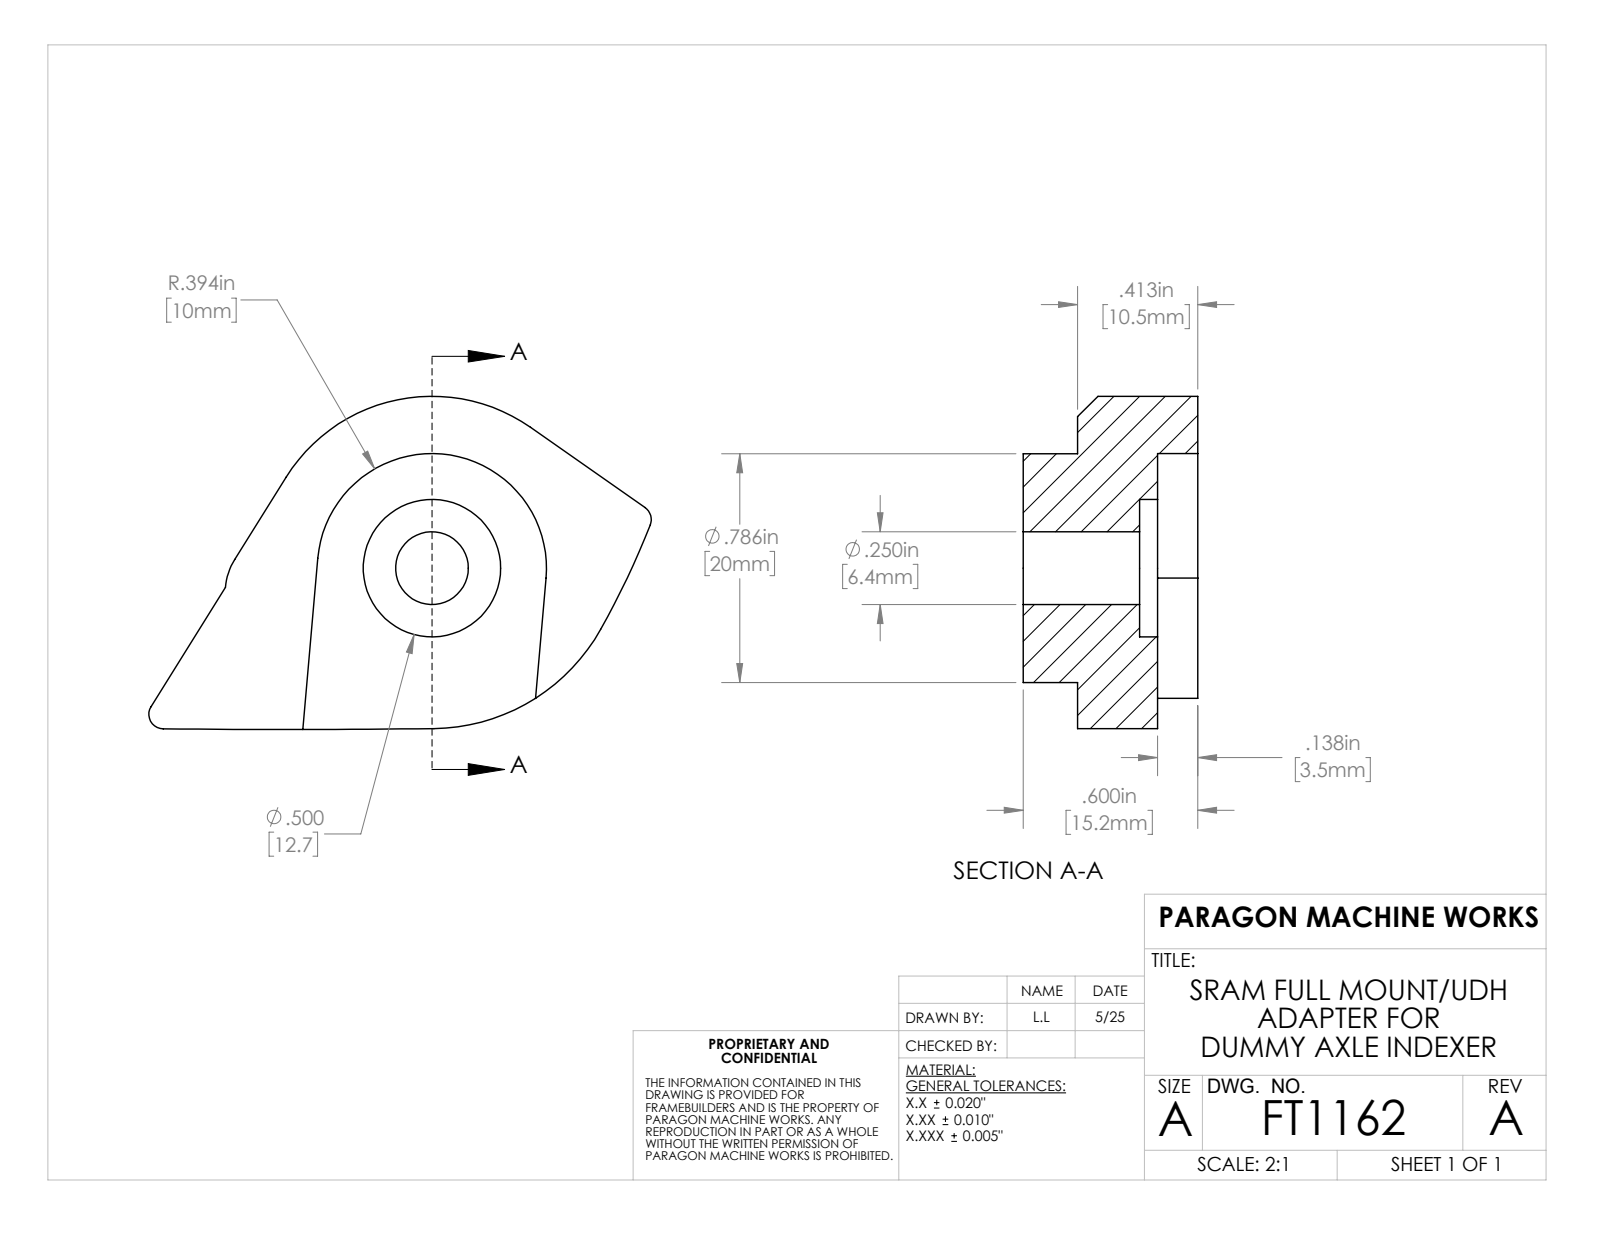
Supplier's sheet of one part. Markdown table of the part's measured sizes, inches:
| quantity | value |
| --- | --- |
| STEP written by | Mastercam 2018 ... CNC Software, Inc. (AUTOMOTIVE_DESIGN) |
| units | inches |
| bodies | 1 solid, 28 faces (13 planar, 13 cylindrical, 2 other) |
| overall size | 6.887 × 1.421 × 0.6 |
| volume | 0.519 in³ |
| surface area | 5.439 in² |
| round holes (diameter × count) | 0.25 × 1, 0.472 × 1 |
| round bosses / shafts (diameter × count) | 0.786 × 1 |
| partial cylindrical surfaces (radius × count) | 0.05 × 2, 0.217 × 1, 0.394 × 1, 0.591 × 1, 0.666 × 1, 2.974 × 1, 39.37 × 1 |
| main face-to-face distances | 0.413, 0.275, 0.138, 0.187, 0.462, 0.6, 0.4, 0.213, 0.062, 0.2 |
